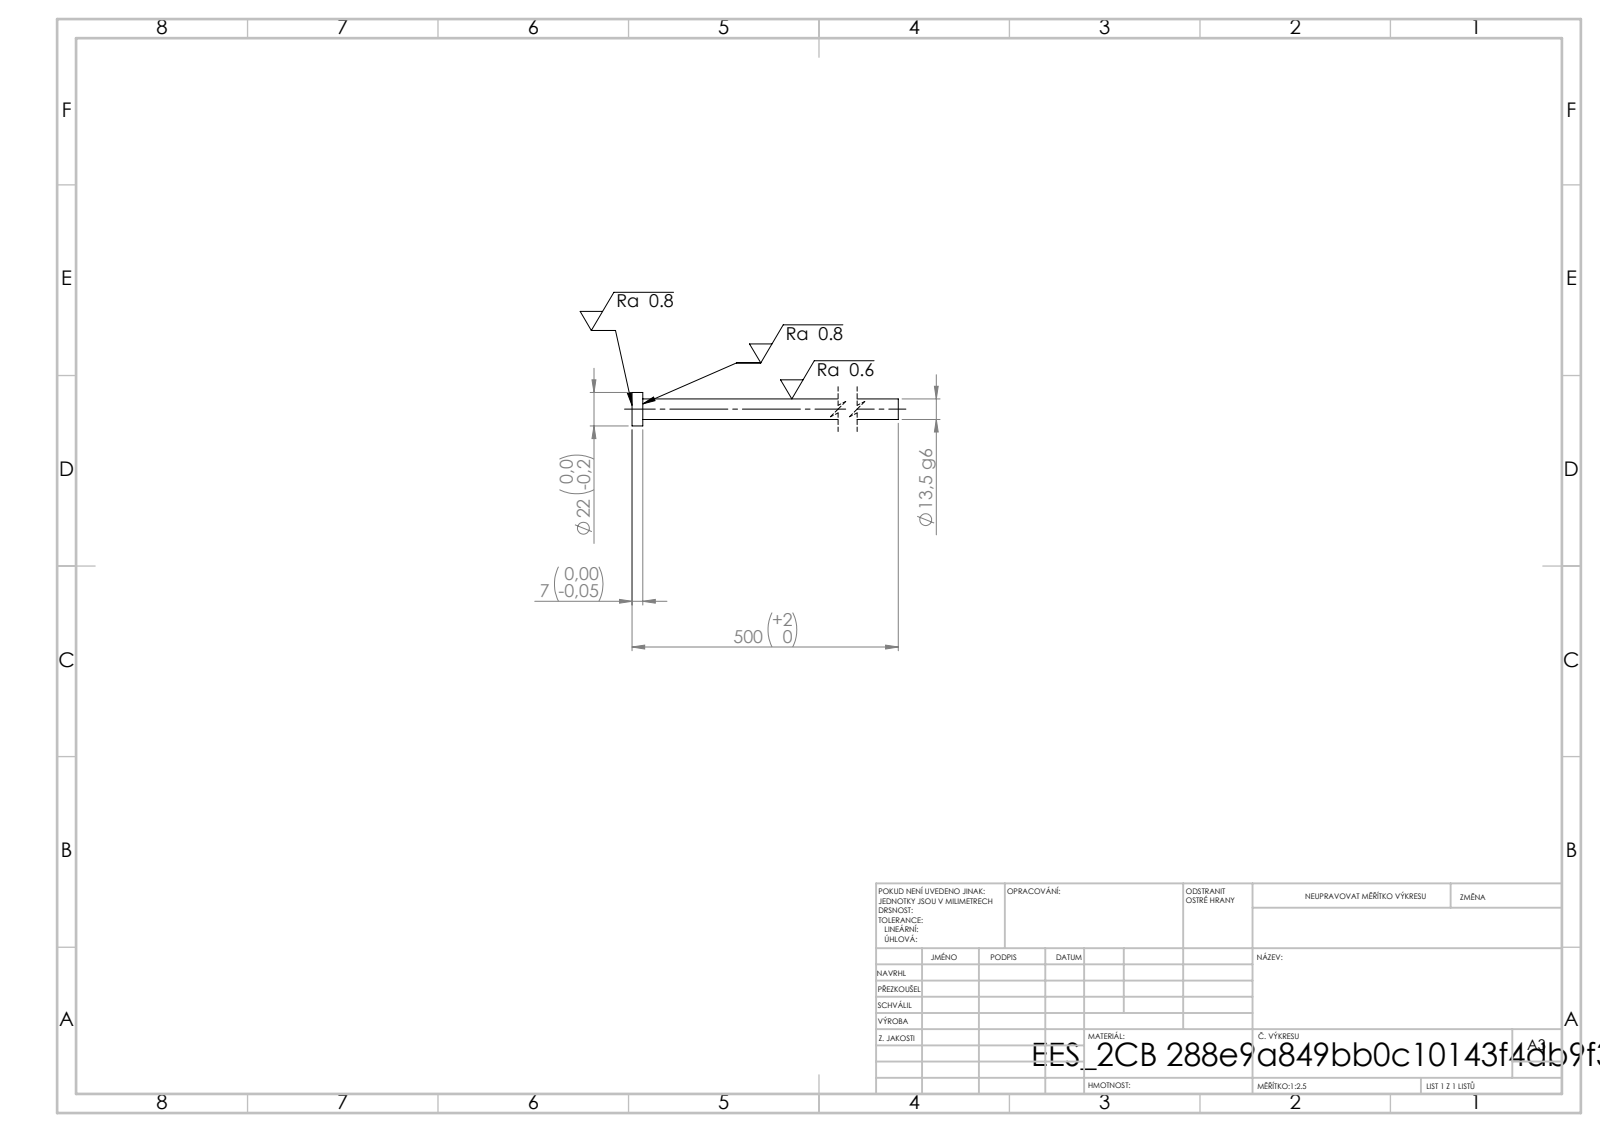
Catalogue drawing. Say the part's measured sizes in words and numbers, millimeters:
Its 3-D file was written by "SolidWorks 2019 (CONFIG_CONTROL_DESIGN)". It is 1 solid with 7 faces: 3 planar, 4 cylindrical and 0 other. Overall it measures 500 by 22 by 22 millimeters. Its volume is 73 228 cubic millimeters and its surface area 22 153 square millimeters. Round bosses or shafts: 1 of diameter 22, 1 of diameter 13.5. The main face-to-face distances are 7, 500, 493.
